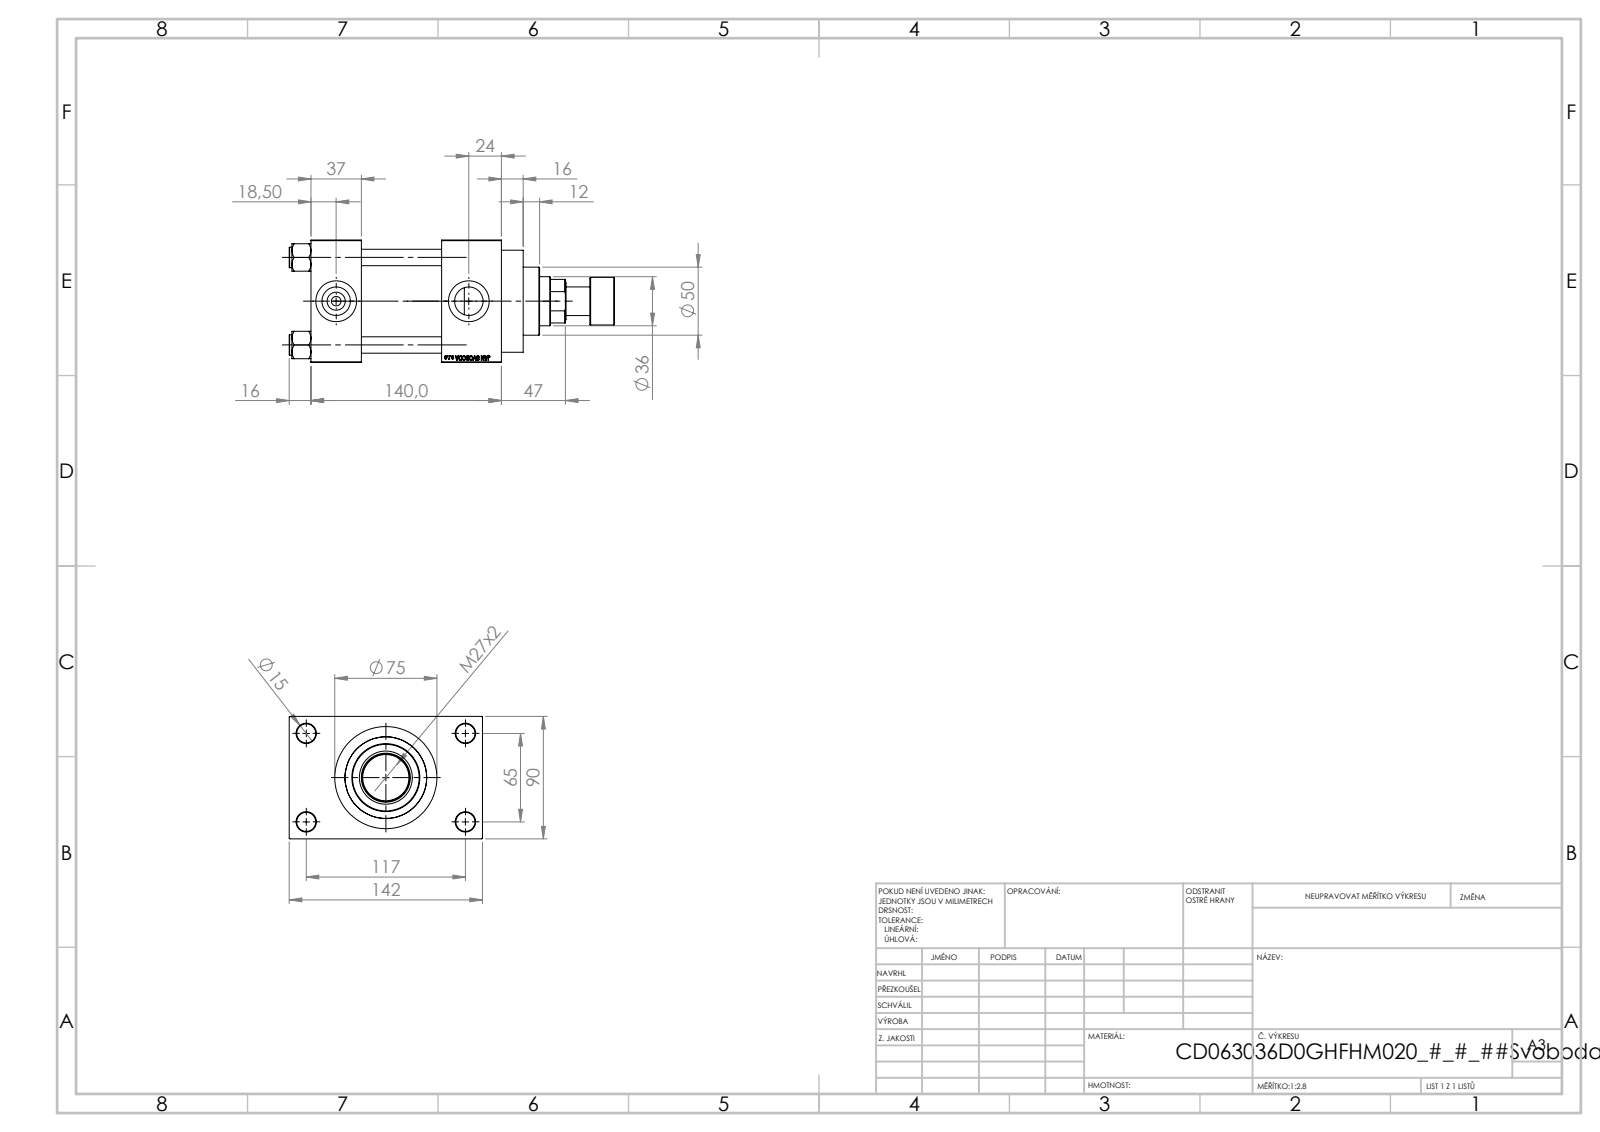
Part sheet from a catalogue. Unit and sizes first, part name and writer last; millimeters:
Units: millimetres
Overall size (bounding box): 239 × 142 × 90
Round holes (diameter × count): ⌀12 ×4, ⌀14 ×4, ⌀7 ×2, ⌀20.96 ×2, ⌀30 ×2, ⌀25.5 ×1, ⌀36 ×1, ⌀39 ×1, ⌀50 ×1, ⌀60 ×1, ⌀63 ×1
Round bosses / shafts (diameter × count): ⌀15 ×4, ⌀75 ×1, ⌀69 ×1, ⌀35 ×1, ⌀21 ×1
Main face-to-face distances: 90, 59, 37, 96, 140, 103, 44, 26, 116, 142
Hole centre spacings: 26.35, 45.47, 64.3, 66.92, 69.81, 90.65, 111.34, 65
Volume: 1 135 000 mm³ · Surface area: 211 351 mm²
Bodies: 12 solids, 1117 faces (501 planar, 92 cylindrical, 524 other)
Part name (STEP PRODUCT): V215CR_ROD_END_F; V215CD_D_Body; V215CD_VC_A; V215CD_D_TYCINKA (+2 more)
STEP written by: SolidWorks 2019 (CONFIG_CONTROL_DESIGN)
